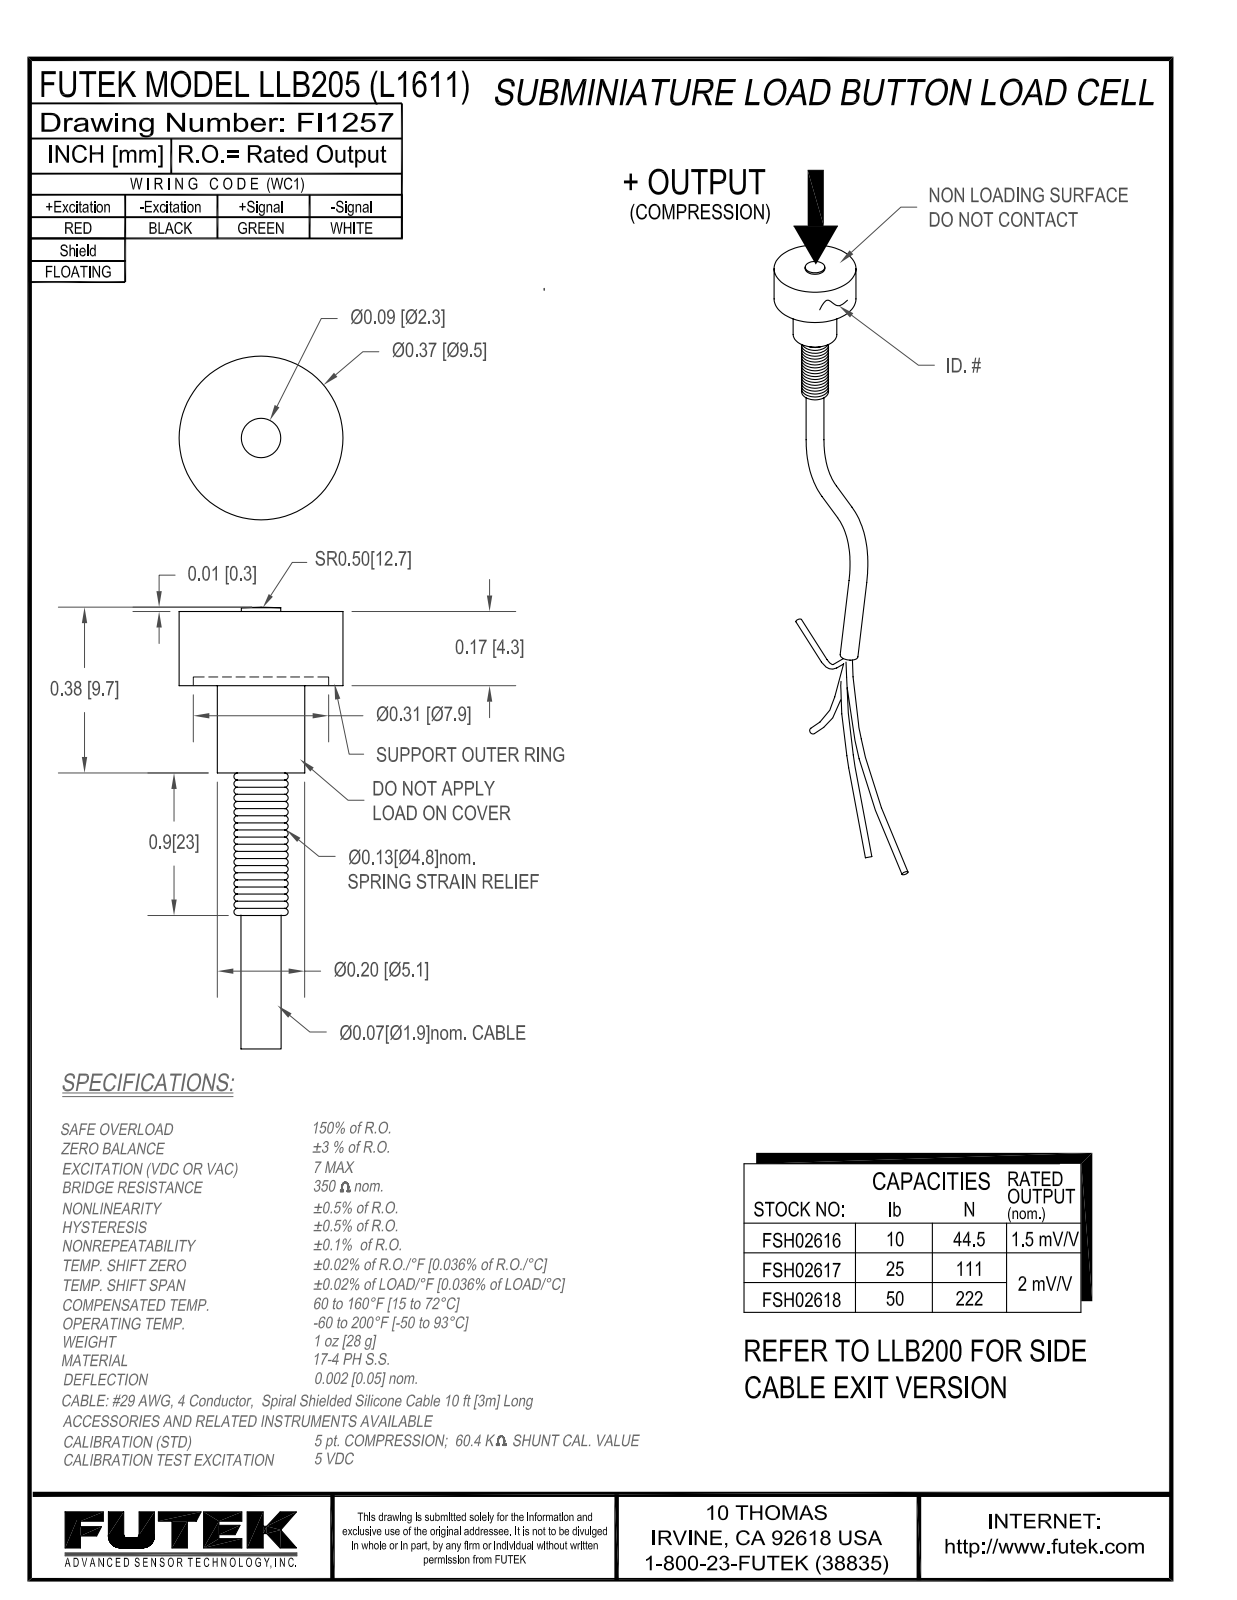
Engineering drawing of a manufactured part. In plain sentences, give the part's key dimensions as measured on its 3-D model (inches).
The part is named "LLB205; CABLE". Its 3-D file was written by "Autodesk Inventor 2008 (AUTOMOTIVE_DESIGN)". It is 1 solid with 90 faces: 10 planar, 8 cylindrical and 72 other. Overall it measures 1.378 by 0.375 by 0.375 inches. Its volume is 0.029 cubic inches and its surface area 1.614 square inches. Round holes: 1 of diameter 0.077, 1 of diameter 0.125, 1 of diameter 0.31. Round bosses or shafts: 1 of diameter 0.375, 1 of diameter 0.3, 1 of diameter 0.2, 1 of diameter 0.09, 1 of diameter 0.079. The main face-to-face distances are 0.02, 0.15, 0.17, 0.18, 0.2, 0.35, 0.22, 0.04, 0.13, 0.83.
